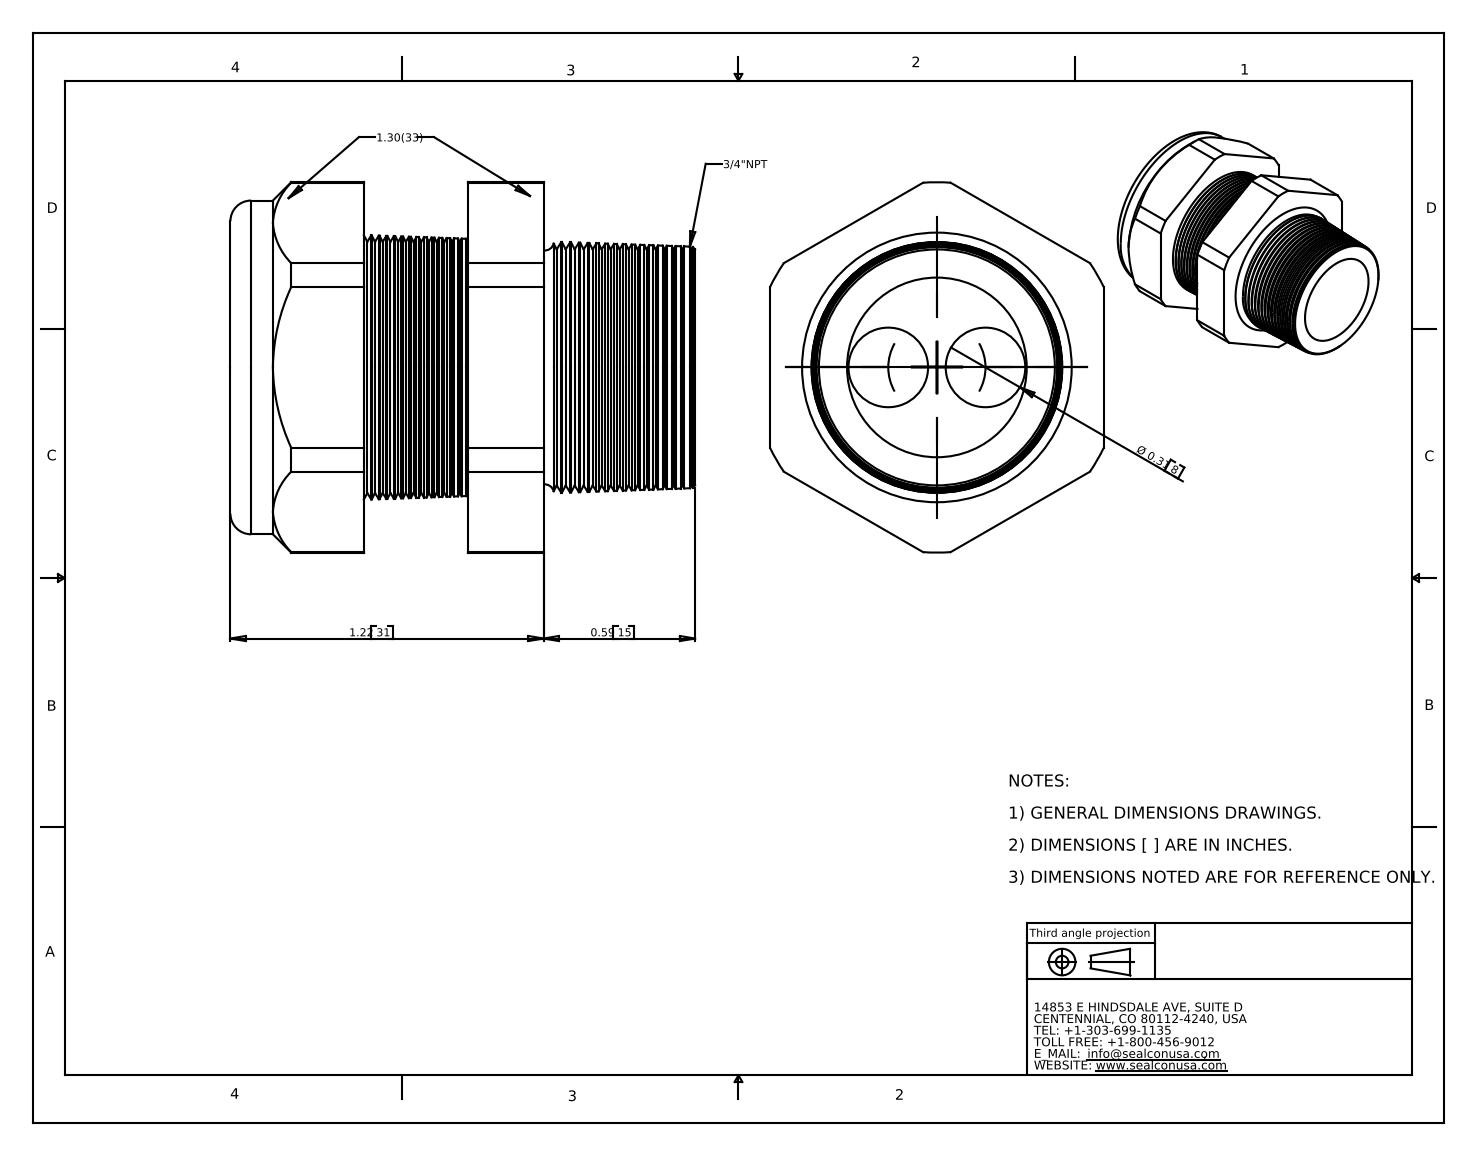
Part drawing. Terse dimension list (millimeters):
name: CD21N3-GY
written by: SolidWorks 2007 (CONFIG_CONTROL_DESIGN)
unit: mm
bodies: 2 solids, 232 faces (20 planar, 24 cylindrical, 188 other)
size: 45 × 36.7 × 33
volume: 20 320 mm³; area: 11 410 mm²
holes: 2× ⌀7.9, 1× ⌀17.5, 1× ⌀18
bosses: 1× ⌀33
rounds: 1× R18.3
face distances: 33, 23.5, 13.2, 10.3, 31, 17.8, 7.5, 45, 31.8, 21.5
hole spacings: 4.8, 9.6
